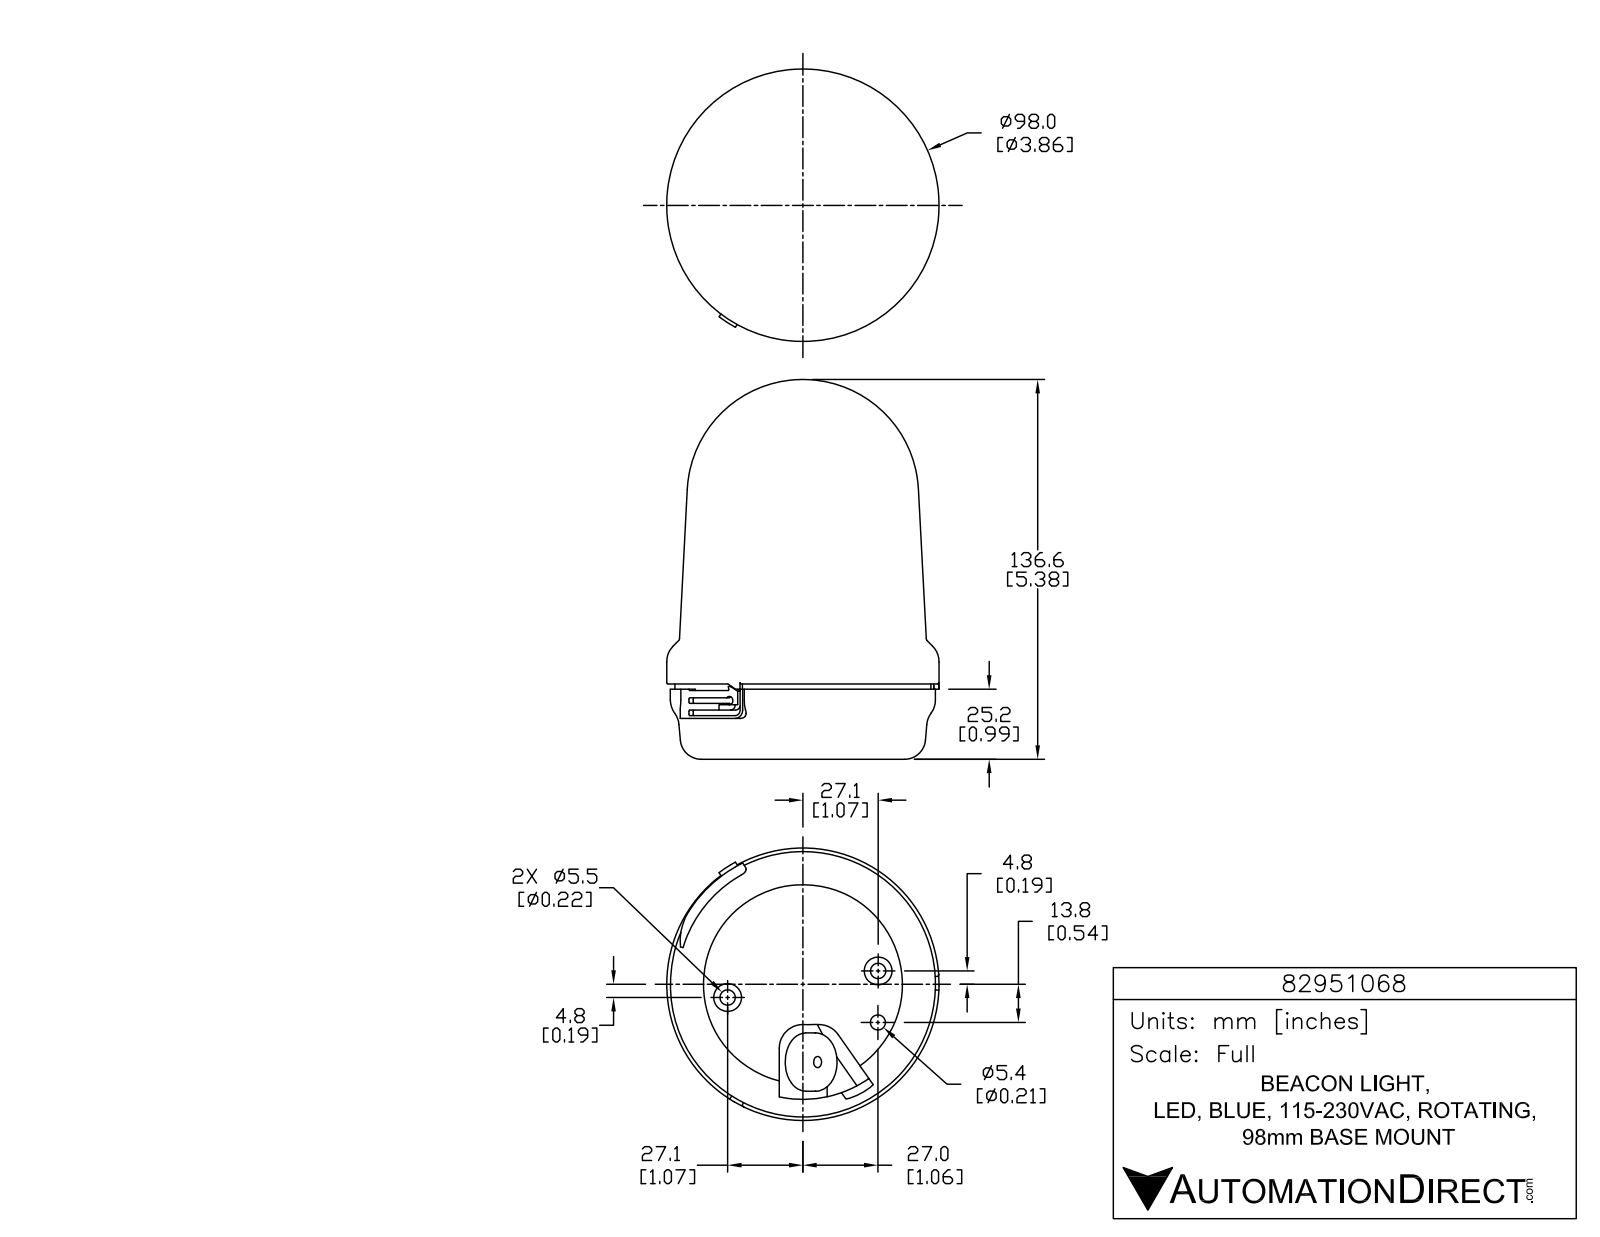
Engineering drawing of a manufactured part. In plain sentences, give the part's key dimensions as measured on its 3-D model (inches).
The part is named "82951068". Its 3-D file was written by "SolidWorks 2015 (AUTOMOTIVE_DESIGN)". It is 1 solid with 872 faces: 566 planar, 204 cylindrical and 102 other. Overall it measures 5.378 by 3.858 by 3.858 inches. Its volume is 44.69 cubic inches and its surface area 73.66 square inches. Round holes: 3 of diameter 0.059, 2 of diameter 0.217, 1 of diameter 0.157, 1 of diameter 0.213, 1 of diameter 2.819. Round bosses or shafts: 3 of diameter 0.339, 3 of diameter 0.084, 2 of diameter 0.394, 1 of diameter 3.858, 1 of diameter 3.756, 1 of diameter 3.626, 1 of diameter 0.827. Partial cylindrical surfaces (rounded edges, fillets, slot ends): 9 of radius 0.005, 6 of radius 0.005, 6 of radius 0.012, 6 of radius 0.012, 6 of radius 0.012, 6 of radius 0.196, 5 of radius 0.02, 4 of radius 0.039. The main face-to-face distances are 1.045, 0.972, 0.073, 0.02, 0.992, 1.065, 0.236, 0.579, 0.559, 0.413. The hole center spacings are 1.083, 0.73, 1.193, 2.158, 2.165.
